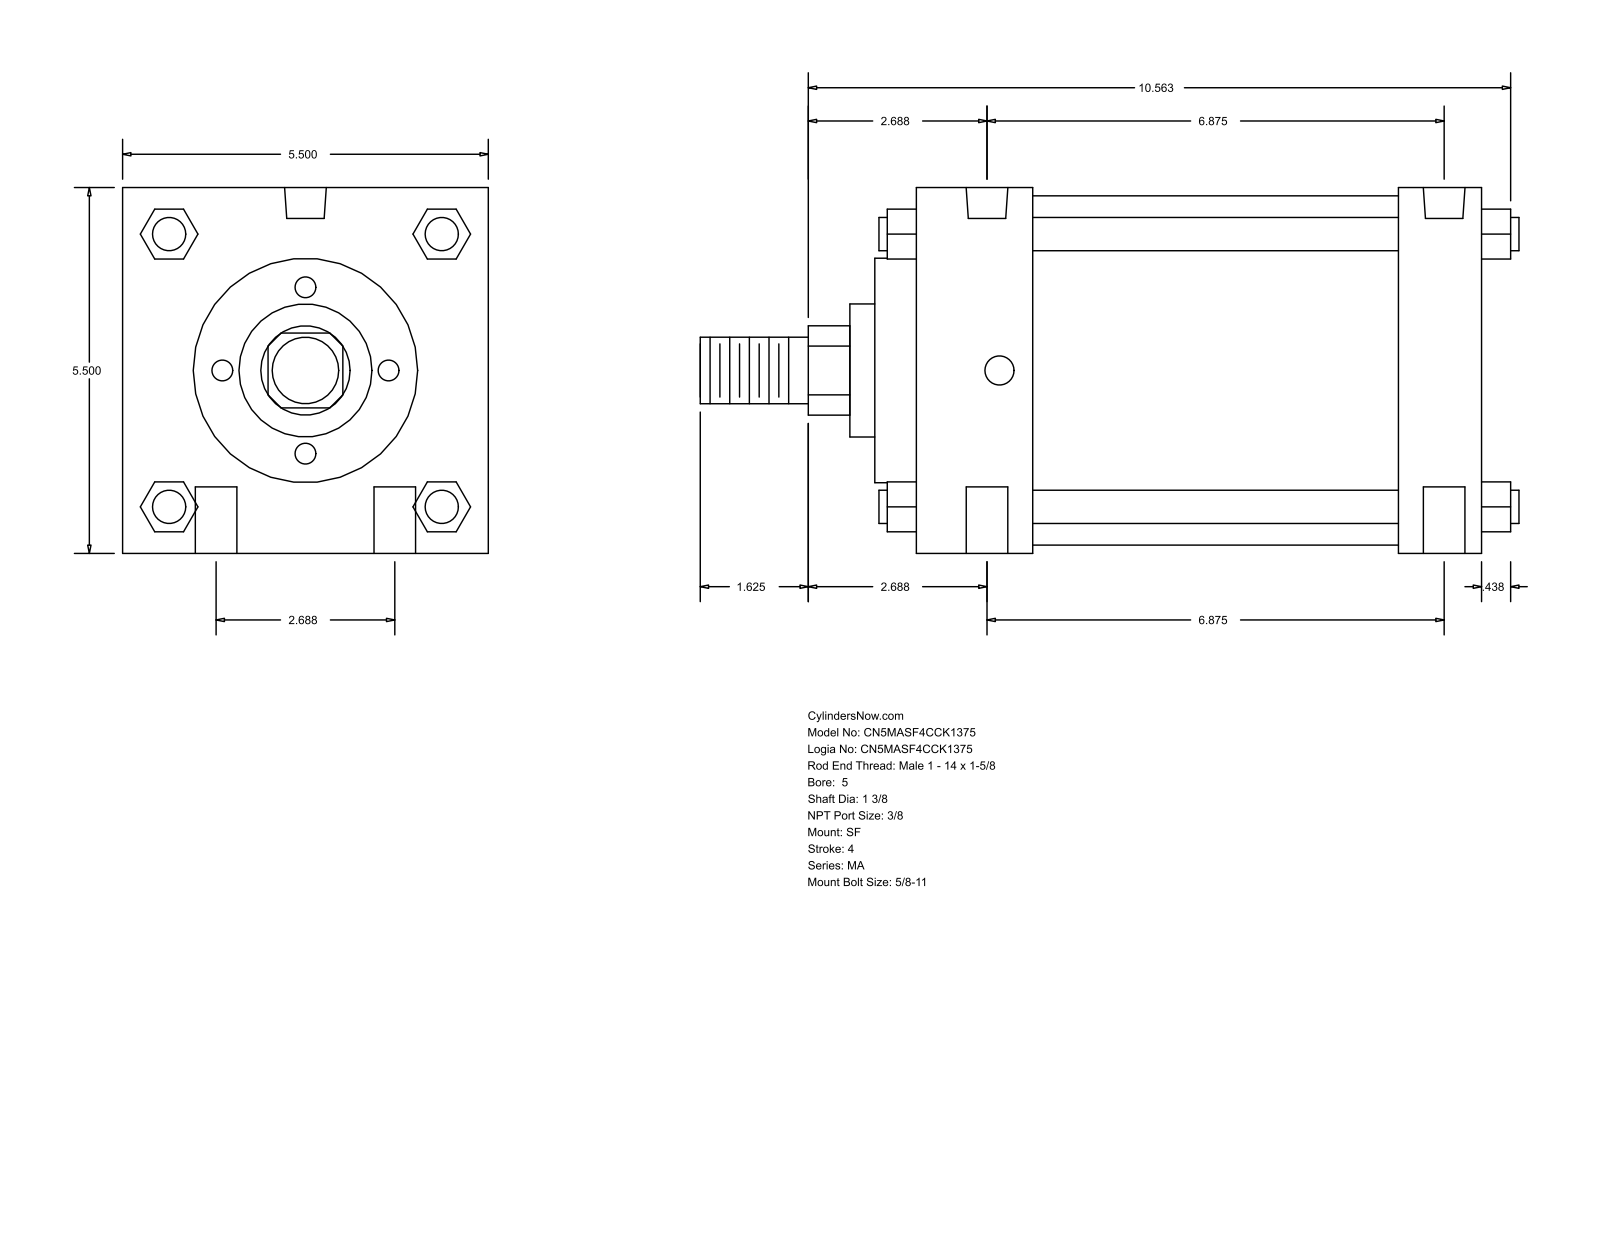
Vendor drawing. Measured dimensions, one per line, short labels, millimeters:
name: MA_SF__0500_1.375
written by: GSSL Pune (CONFIG_CONTROL_DESIGN)
unit: mm
bodies: 0 solids, 126 faces (95 planar, 31 cylindrical, 0 other)
size: 312.74 × 139.7 × 139.7
holes: 4× ⌀15.88, 2× ⌀11.11, 2× ⌀15.93
bosses: 4× ⌀12.7, 1× ⌀133.35, 1× ⌀85.72, 1× ⌀50.8, 1× ⌀34.92, 1× ⌀25.4
rounds: 1× R17.06
face distances: 139.7, 215.91, 44.45, 184.16, 139.71, 171.46, 31.75, 15.87, 60.32, 200.03
hole spacings: 34.13, 177.93, 174.63, 68.26, 187.5, 165.09
